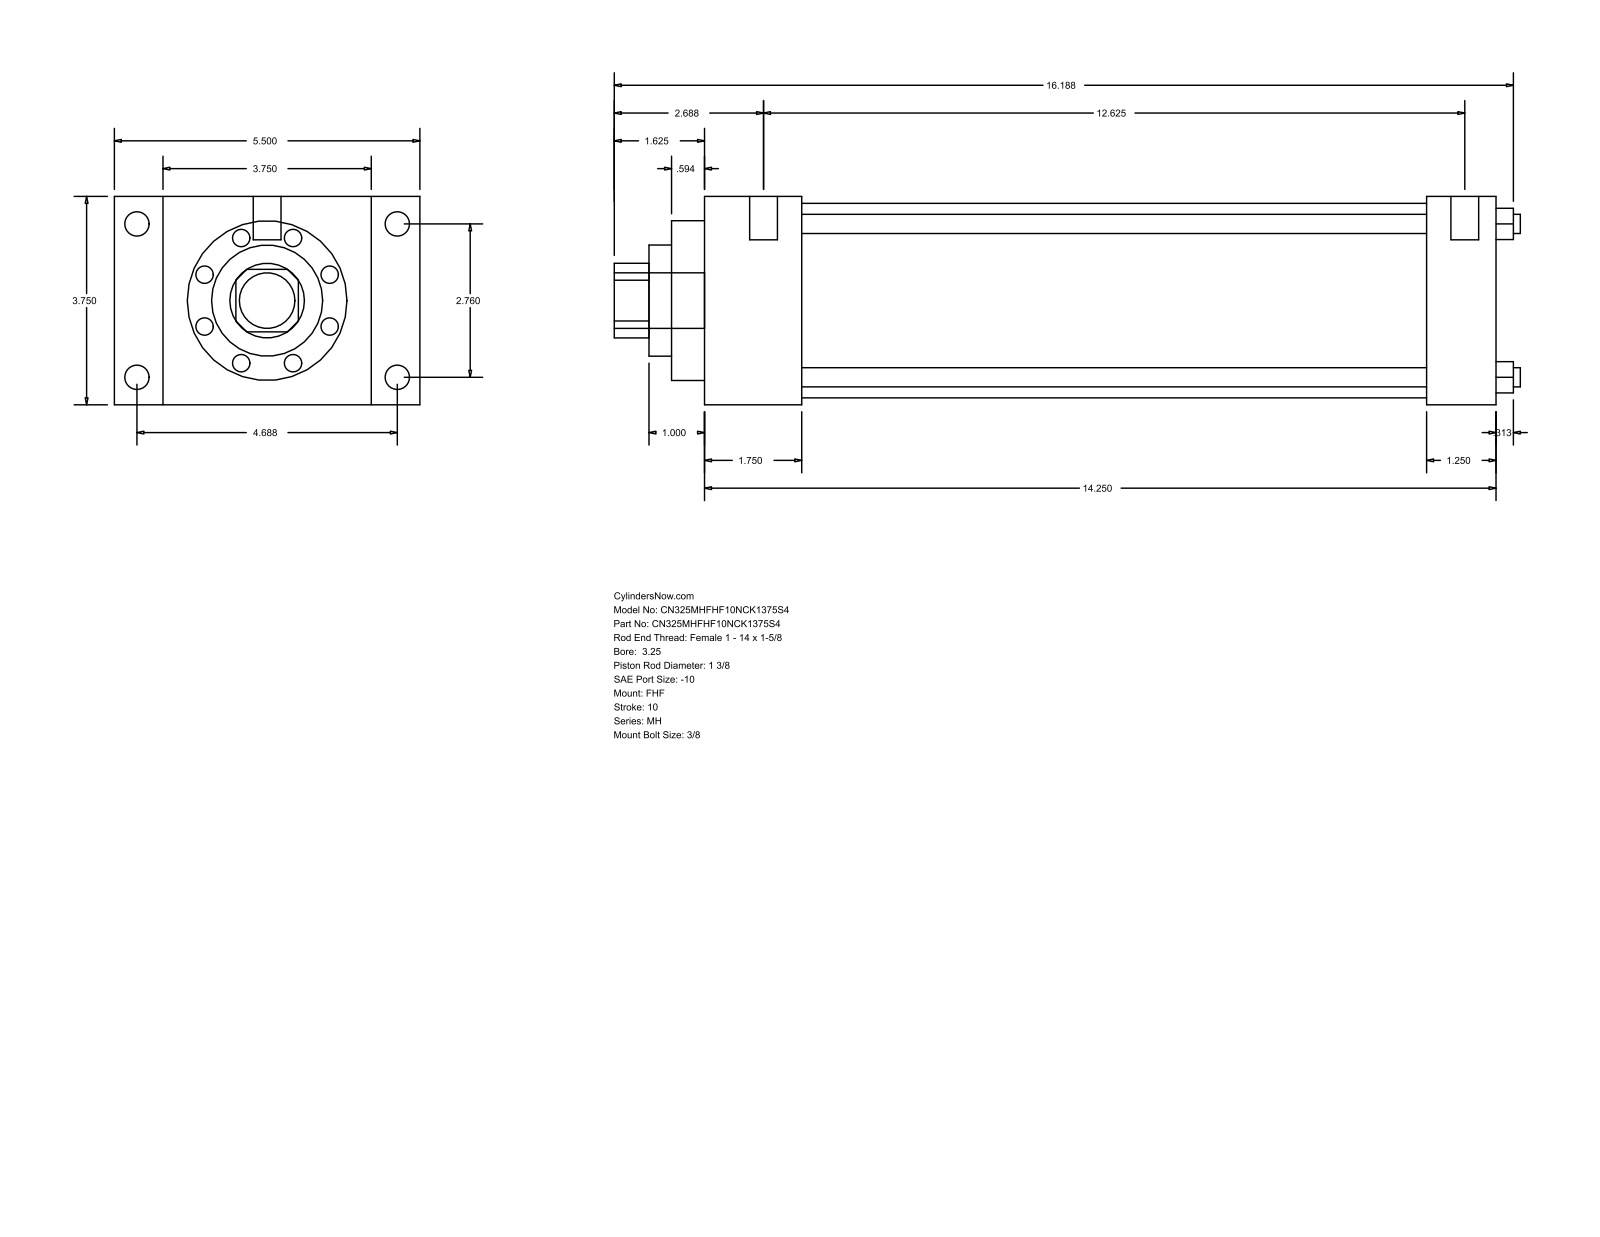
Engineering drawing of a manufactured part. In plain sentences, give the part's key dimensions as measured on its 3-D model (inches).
The part is named "MH_FHF__0325_1.375". Its 3-D file was written by "GSSL Pune (CONFIG_CONTROL_DESIGN)". It is 0 solids with 90 faces: 61 planar, 29 cylindrical and 0 other. Overall it measures 16.313 by 5.5 by 3.75 inches. Round holes: 4 of diameter 0.345, 1 of diameter 1.375, 1 of diameter 2, 1 of diameter 2.875, 1 of diameter 3.5. Round bosses or shafts: 4 of diameter 0.438, 4 of diameter 0.219, 2 of diameter 0.5, 1 of diameter 1. Partial cylindrical surfaces (rounded edges, fillets, slot ends): 1 of radius 0.672. The main face-to-face distances are 3.75, 14.25, 1.75, 12.5, 0.875, 4.625, 5.5, 13, 11.25, 1.25. The hole center spacings are 1.952, 2.76, 3.903.
